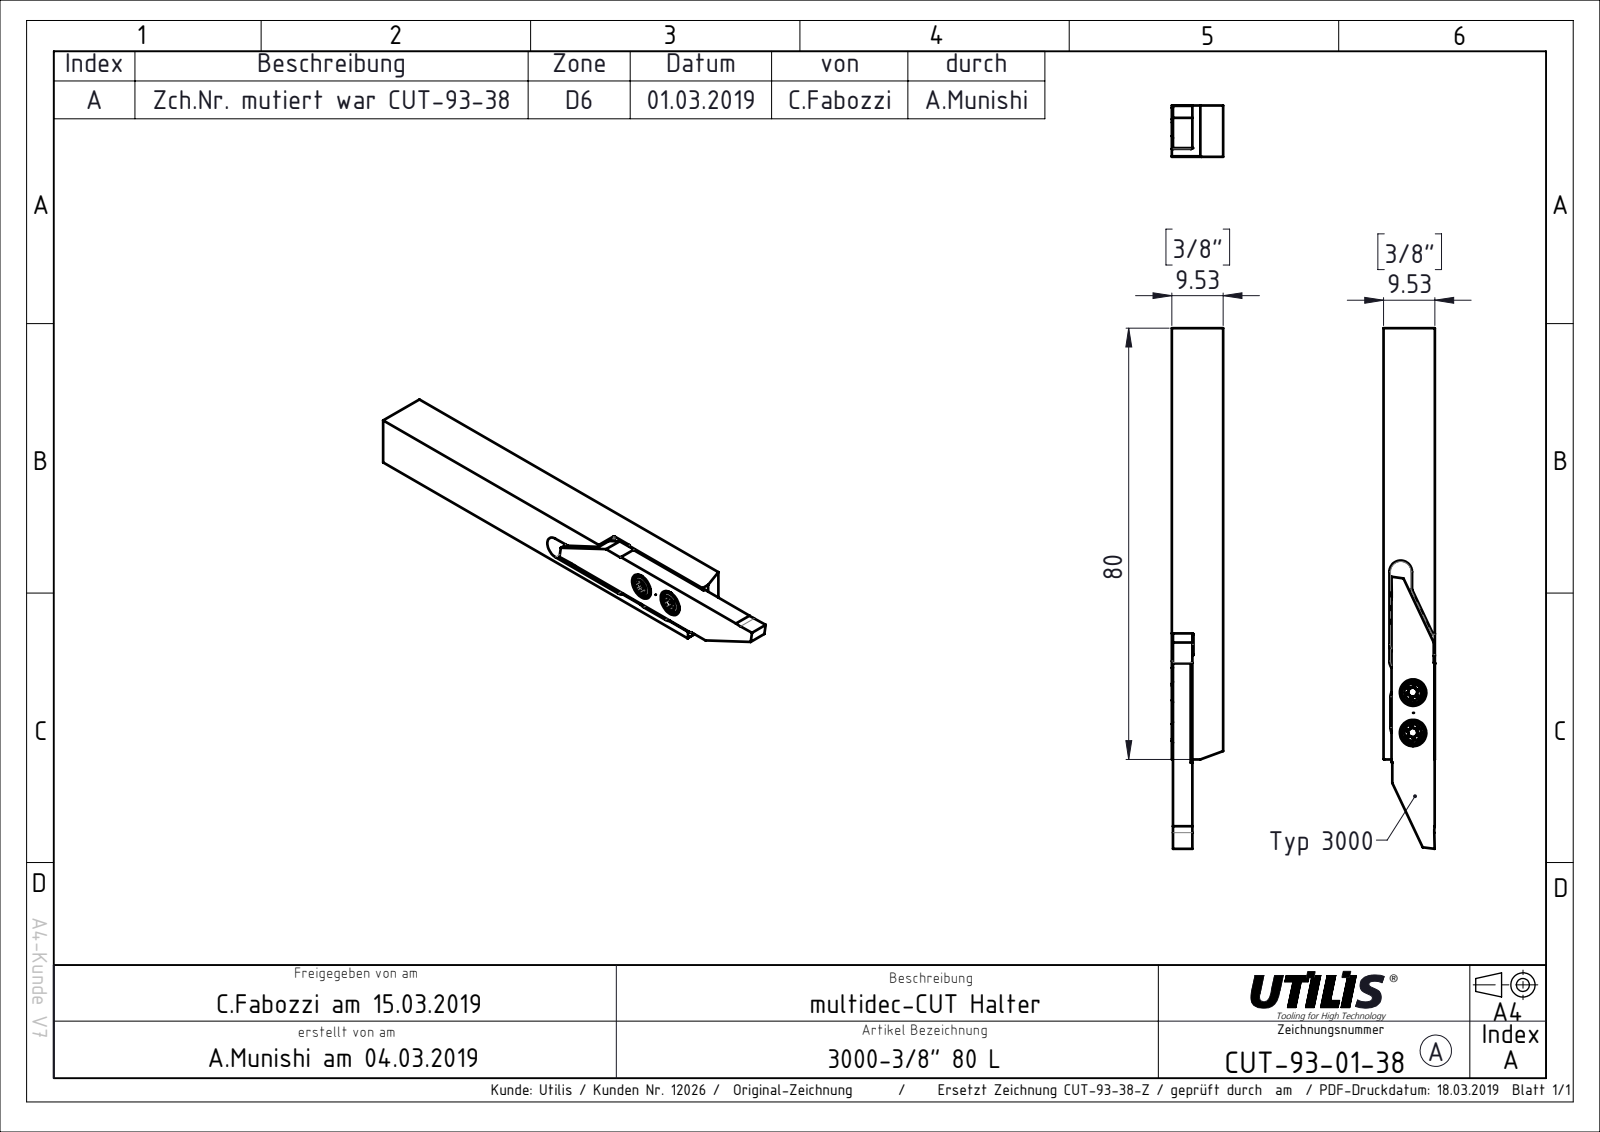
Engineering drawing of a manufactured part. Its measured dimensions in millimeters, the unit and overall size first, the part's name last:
Units: millimetres
Overall size (bounding box): 96.5 × 9.53 × 9.53
Round holes (diameter × count): ⌀2.5 ×2, ⌀4.9 ×2
Partial cylindrical surfaces — rounded edges, fillets, slot ends (radius × count): R2.1 ×4, R0.15 ×2, R10 ×2
Main face-to-face distances: 9.53, 5.73, 3.8, 3.6, 9.33, 1.53, 8, 1.08, 0.45, 8.45
Hole centre spacings: 3.75, 7.5
Volume: 7 222 mm³ · Surface area: 4 441 mm²
Bodies: 2 solids, 55 faces (36 planar, 19 cylindrical, 0 other)
Part name (STEP PRODUCT): CUT-93-Kunde; CUT-93-38; CUT-Vorlage 3000 R+L Lang Kunde_L-Lang; CUT-93-Kunde_38 (+1 more)
STEP written by: SolidWorks 2015 (CONFIG_CONTROL_DESIGN)
